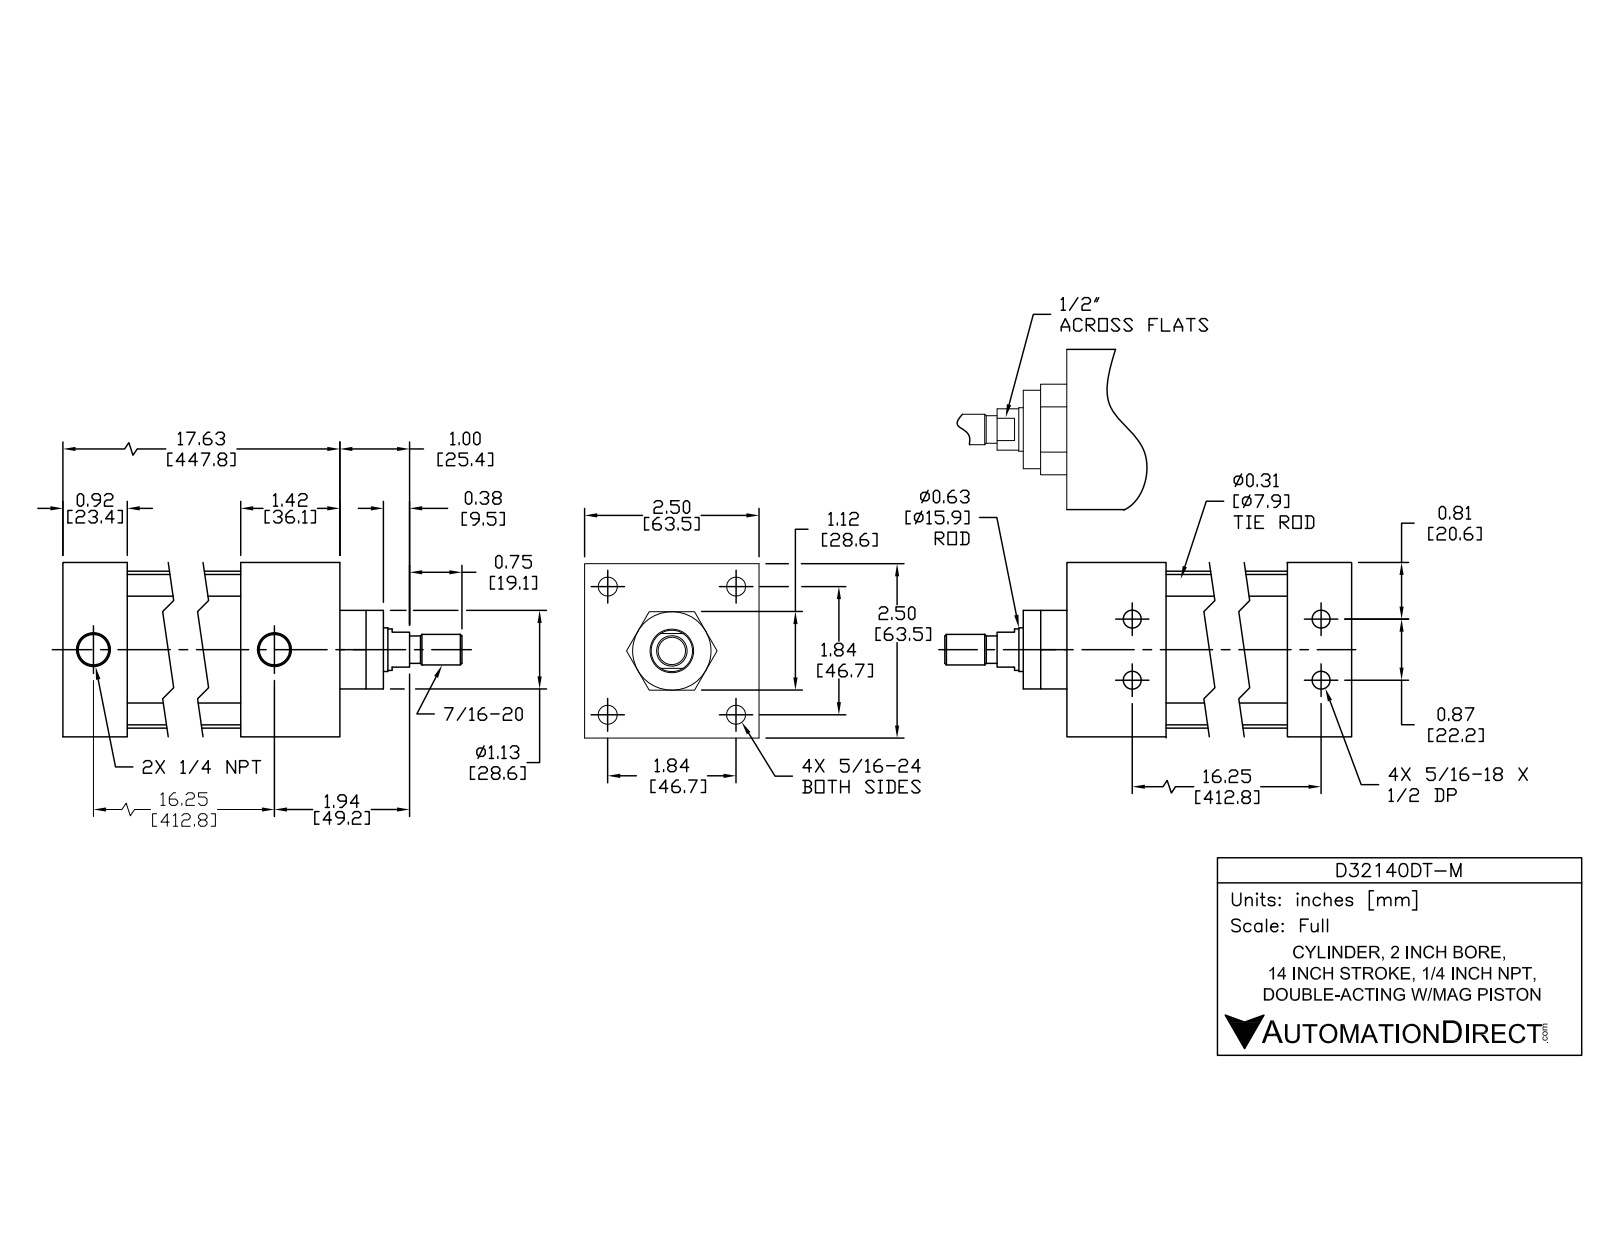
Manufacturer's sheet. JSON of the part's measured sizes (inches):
{"part_name": "D32140DT-M; D32140DT-M BODY; D32140DT-M PISTON", "step_written_by": "SolidWorks 2015 (AUTOMOTIVE_DESIGN)", "units": "inches", "bodies": {"solids": 12, "faces": 298, "planar": 94, "cylindrical": 114, "other": 90}, "overall_size": [19.371, 2.5, 2.5], "volume_in3": 39.27, "surface_area_in2": 387.4, "round_holes": [[0.252, 4], [0.267, 4], [0.359, 4], [0.5, 4], [0.297, 2], [0.477, 2], [0.625, 1], [0.628, 1], [2, 1]], "round_bosses_or_shafts": [[0.484, 4], [0.313, 4], [0.282, 4], [2.25, 1], [1.997, 1], [1.12, 1], [0.622, 1], [0.59, 1]], "partial_cylinders_radius": [[0.25, 4]], "face_to_face_distances": [2.5, 0.08, 15.201, 17.621, 1.42, 16.201, 16.701, 15.281, 0.92, 1], "hole_center_spacings": [1.307, 1.848, 16.251, 16.245, 0.437, 0.438, 0.875, 2.613]}
